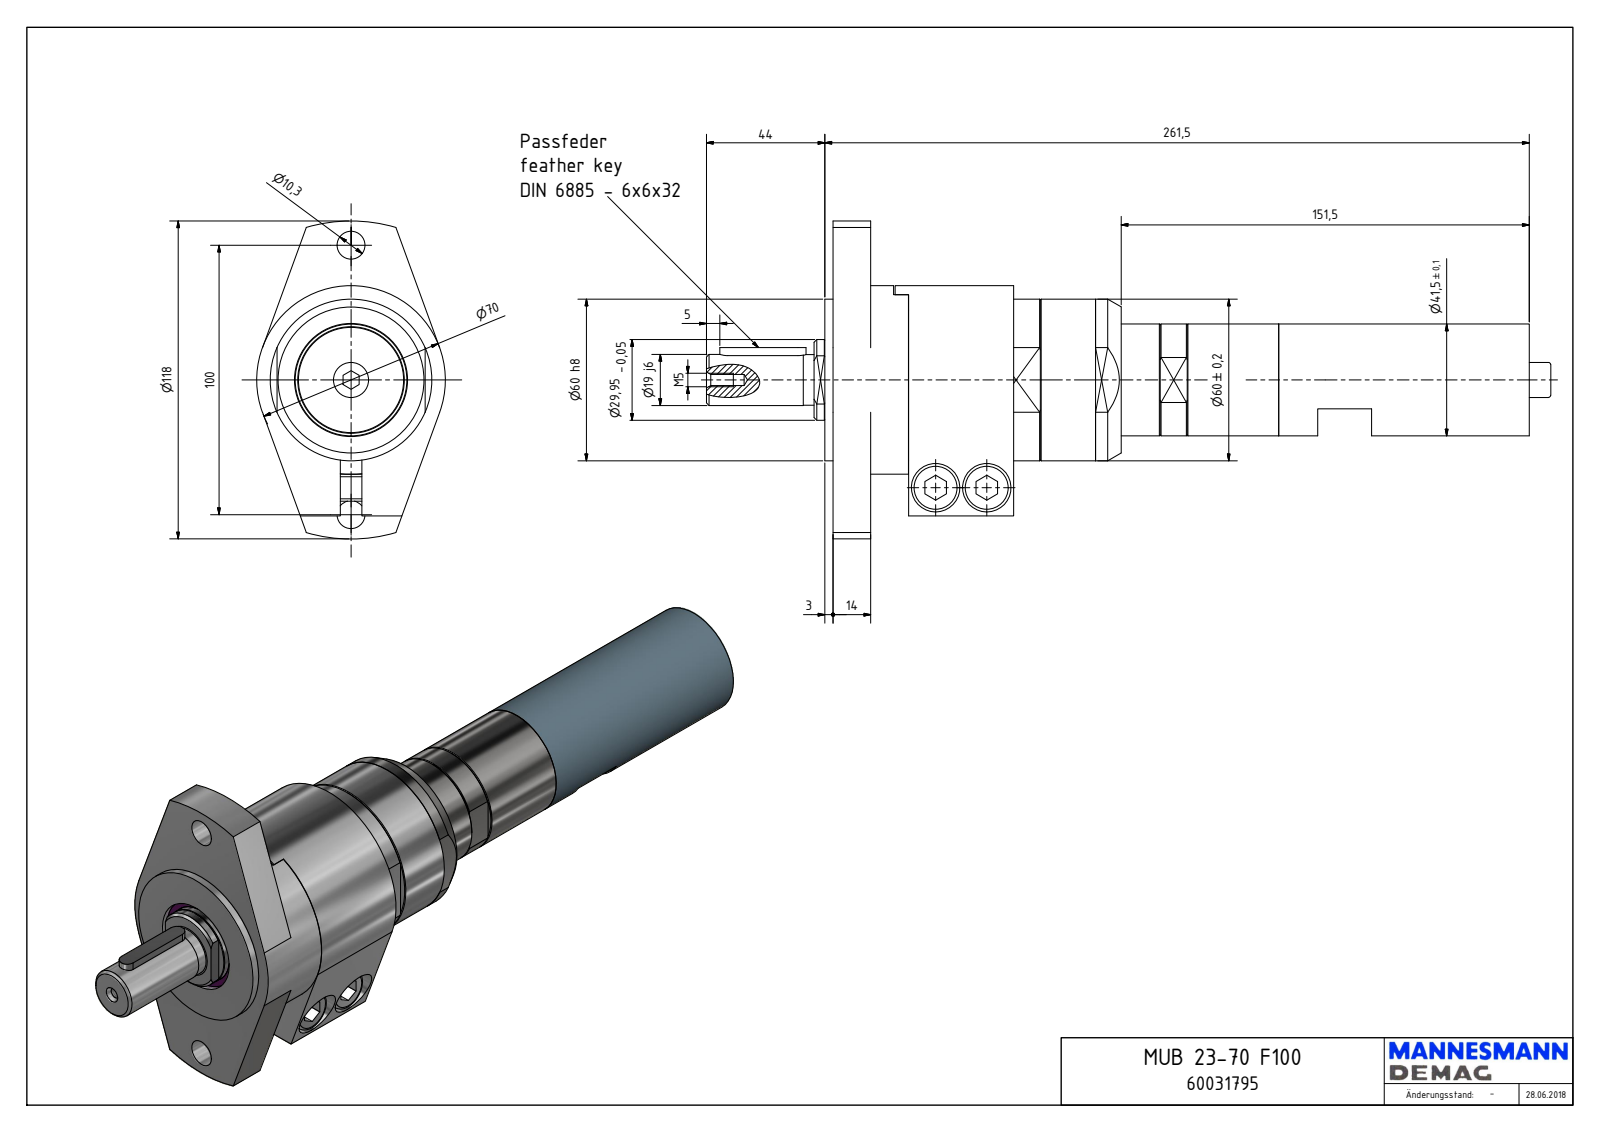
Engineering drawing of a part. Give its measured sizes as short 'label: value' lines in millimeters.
name: MUB 23-70 F100_60031795
written by: Autodesk Inventor 2018 (AUTOMOTIVE_DESIGN)
unit: mm
bodies: 1 solid, 249 faces (120 planar, 81 cylindrical, 48 other)
size: 313.5 × 118 × 70
volume: 642 783 mm³; area: 81 004 mm²
holes: 2× ⌀8.38, 2× ⌀8.57, 2× ⌀10.3, 2× ⌀10.5, 2× ⌀18, 1× ⌀1.55, 1× ⌀4, 1× ⌀4.13, 1× ⌀5.5, 1× ⌀8.5, 1× ⌀35, 1× ⌀36.5
bosses: 2× ⌀16, 2× ⌀10, 1× ⌀70, 1× ⌀60, 1× ⌀55.18, 1× ⌀50.18, 1× ⌀41.5, 1× ⌀39
rounds: 2× R1, 2× R1.6, 2× R2, 2× R2.5, 2× R3, 1× R8, 1× R8.1, 1× R13.02
face distances: 14, 3, 17, 70.1, 39, 67.1, 53.1, 31.1, 28.1, 14.1
hole spacings: 50, 126.91, 19, 20.5, 100
